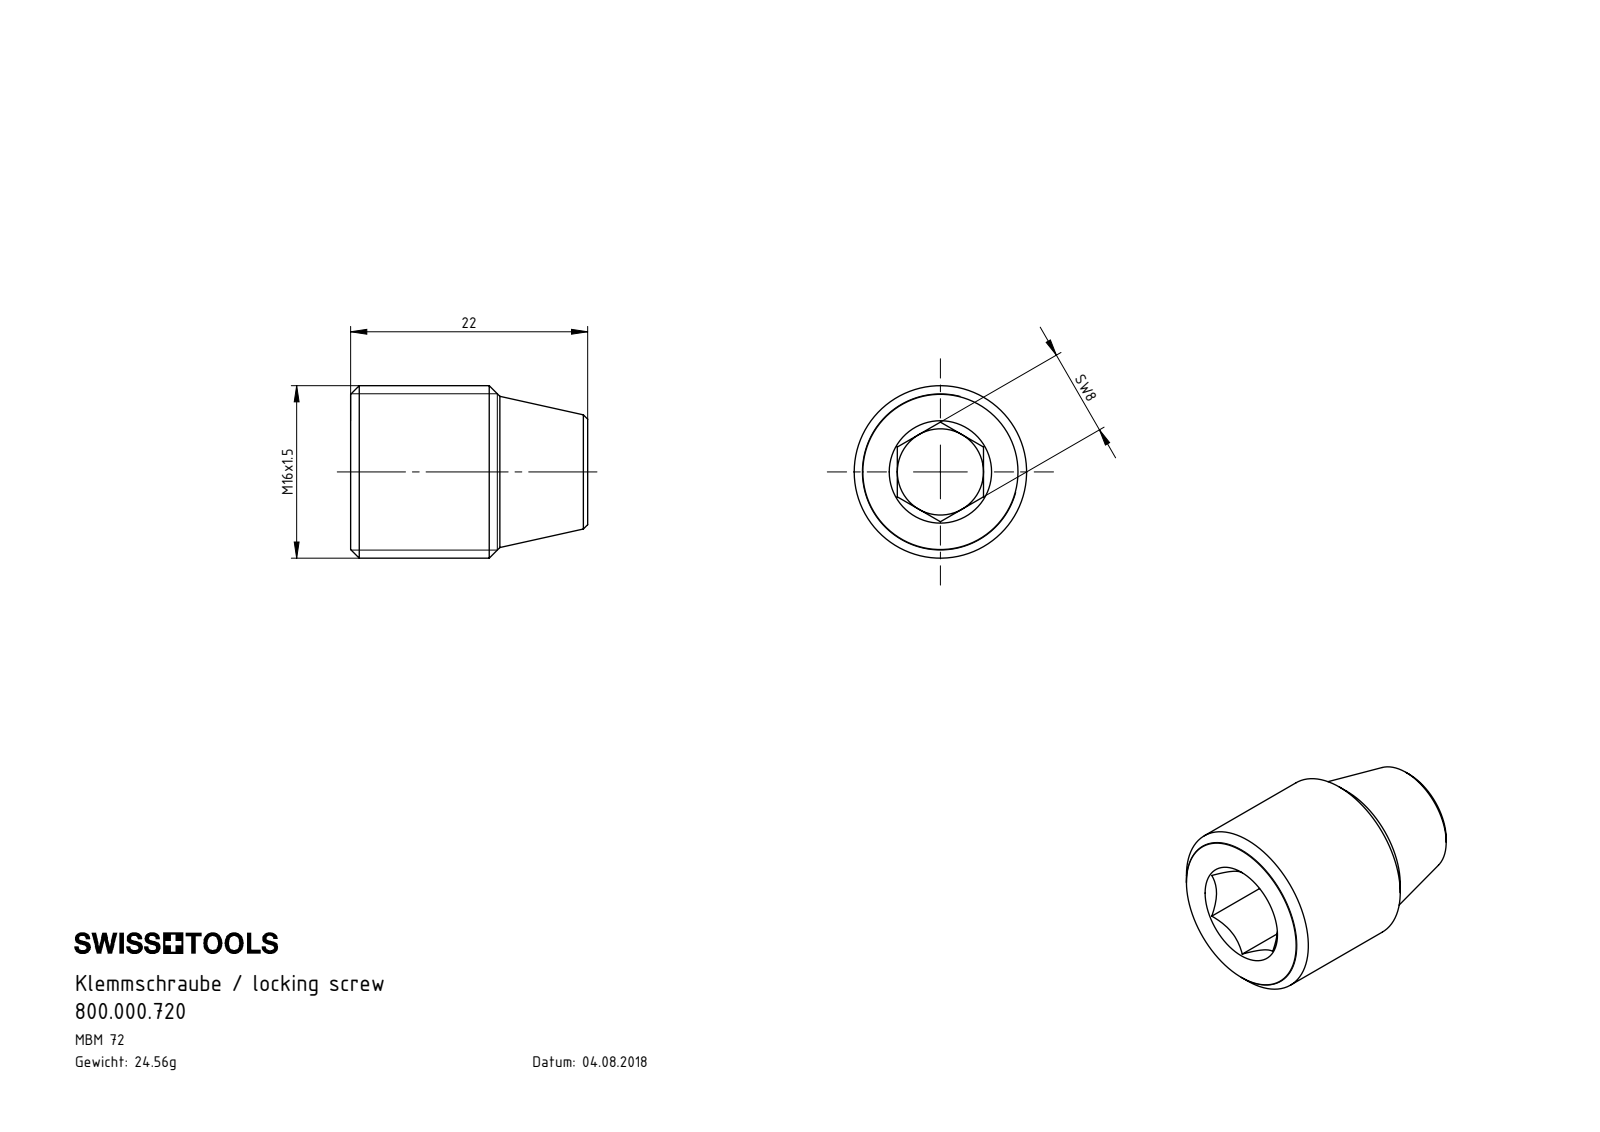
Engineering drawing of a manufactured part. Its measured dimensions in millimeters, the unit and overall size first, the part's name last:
Units: millimetres
Overall size (bounding box): 22 × 16 × 16
Round holes (diameter × count): ⌀8 ×1
Round bosses / shafts (diameter × count): ⌀16 ×1
Main face-to-face distances: 8, 22, 13, 9
Volume: 3 128 mm³ · Surface area: 1 559 mm²
Bodies: 1 solid, 22 faces (14 planar, 2 cylindrical, 6 other)
Part name (STEP PRODUCT): 800.000.720
STEP written by: SolidWorks 2017 (AUTOMOTIVE_DESIGN)
